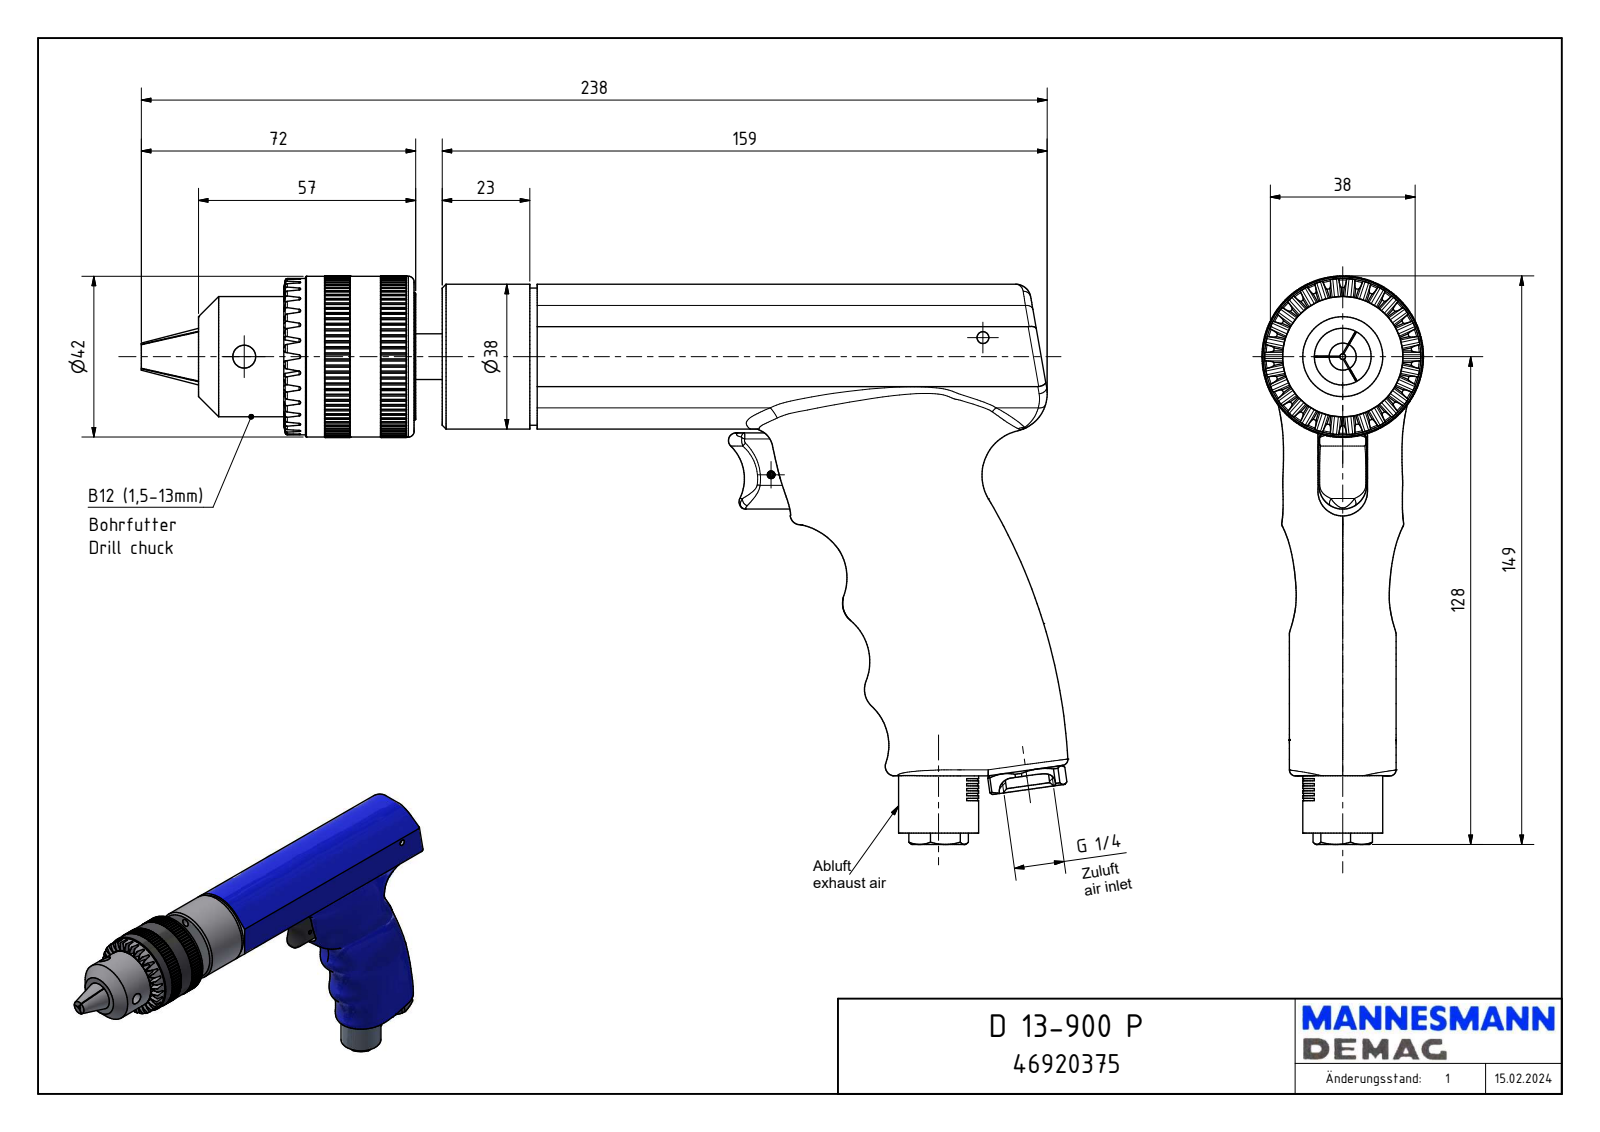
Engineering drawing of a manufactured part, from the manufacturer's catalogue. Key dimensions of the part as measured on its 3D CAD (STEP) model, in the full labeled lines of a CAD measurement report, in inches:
Part name (STEP PRODUCT): D 13-900 P_46920375
STEP written by: Autodesk Inventor 2008 (AUTOMOTIVE_DESIGN)
Units: inches
Bodies: 1 solid, 1631 faces (693 planar, 337 cylindrical, 601 other)
Overall size (bounding box): 9.574 × 5.874 × 1.669
Volume: 22.33 in³ · Surface area: 79.51 in²
Round holes (diameter × count): ⌀0.059 ×1, ⌀0.122 ×1, ⌀0.252 ×1, ⌀0.492 ×1, ⌀0.669 ×1, ⌀0.945 ×1, ⌀1.425 ×1
Round bosses / shafts (diameter × count): ⌀1.661 ×1, ⌀1.614 ×1, ⌀1.496 ×1, ⌀1.417 ×1, ⌀1.322 ×1, ⌀1.242 ×1, ⌀0.827 ×1, ⌀0.656 ×1
Partial cylindrical surfaces — rounded edges, fillets, slot ends (radius × count): R0.02 ×75, R0.079 ×6, R0.063 ×4, R0.256 ×2, R0.013 ×1, R0.018 ×1, R0.022 ×1, R0.026 ×1
Main face-to-face distances: 1.496, 0.284, 0.492, 1.004, 0.016, 0.3, 0.502, 0.748, 3.626, 3.91
